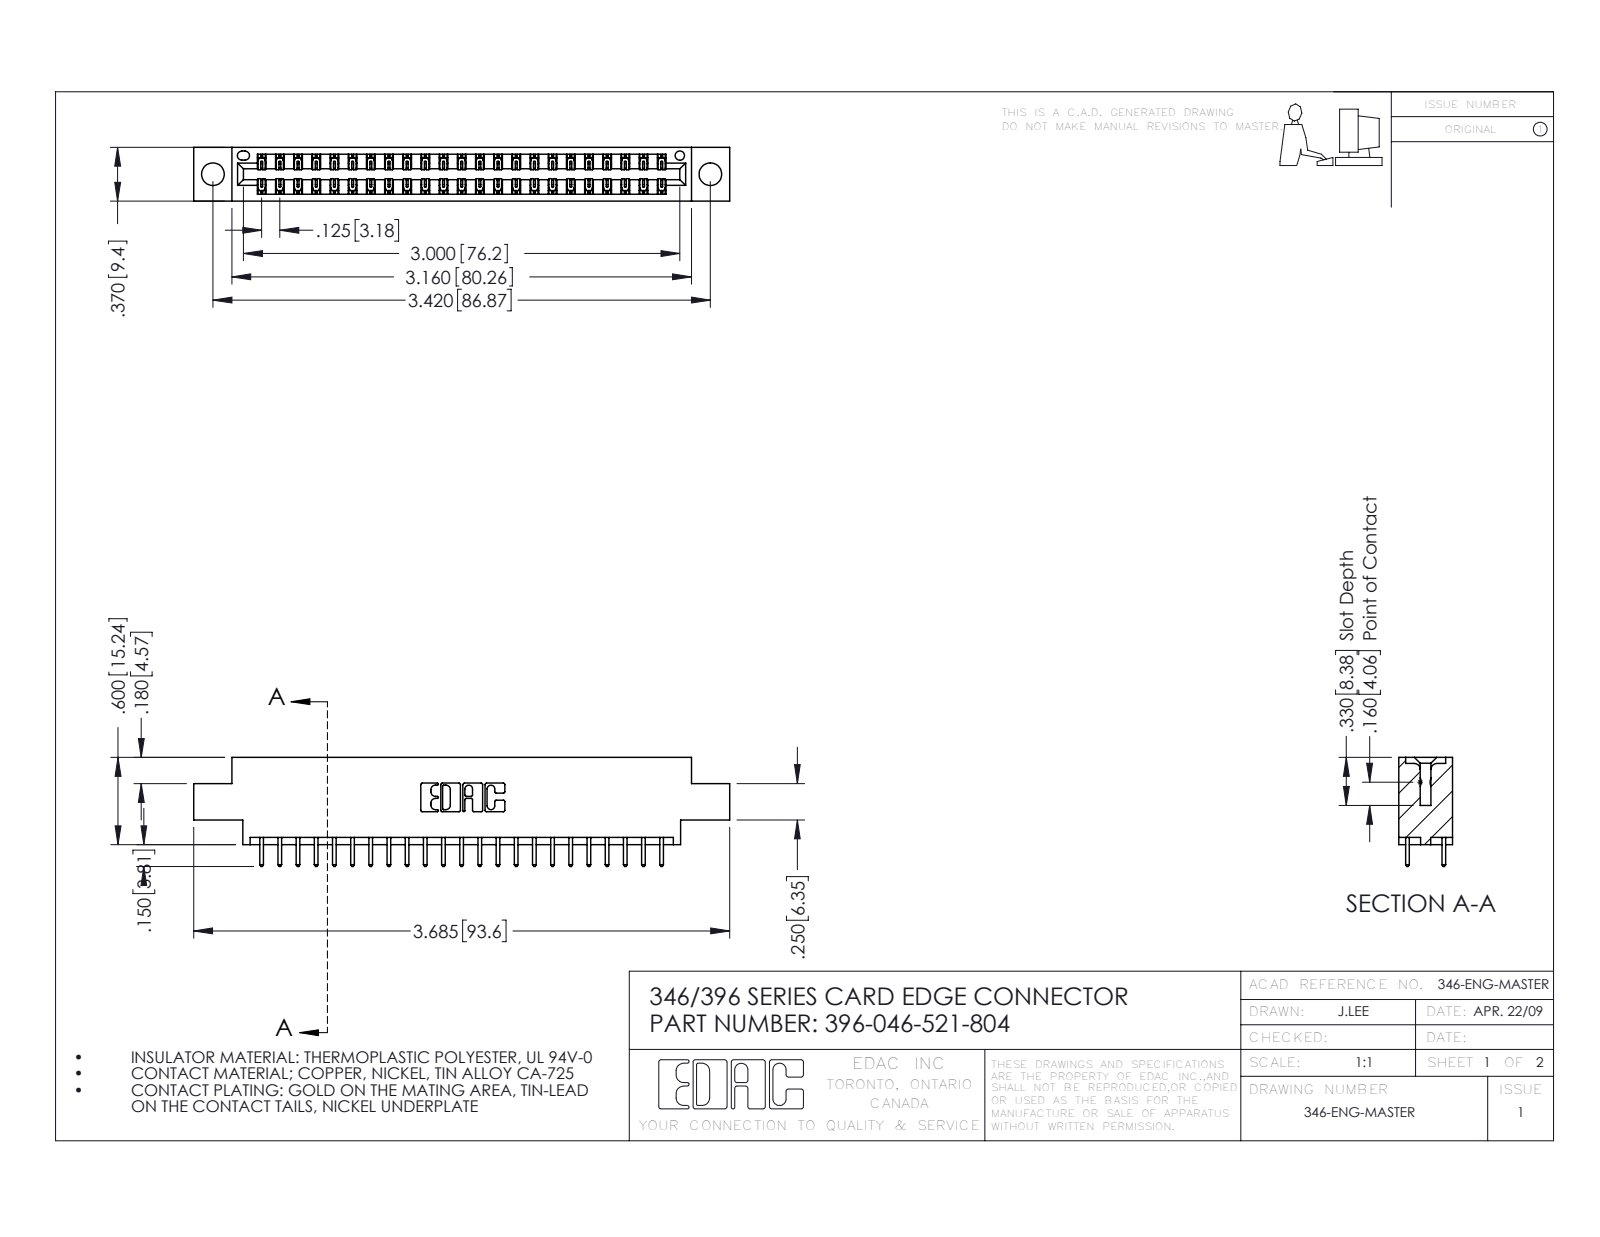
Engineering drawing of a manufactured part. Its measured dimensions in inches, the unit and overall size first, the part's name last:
Units: inches
Overall size (bounding box): 3.685 × 0.75 × 0.37
Round holes (diameter × count): ⌀0.156 ×2, ⌀0.064 ×1
Partial cylindrical surfaces — rounded edges, fillets, slot ends (radius × count): R0.006 ×69, R0.01 ×46, R0.01 ×22, R0.007 ×6, R0.031 ×6, R0.026 ×3, R0.014 ×2, R0.022 ×2
Main face-to-face distances: 0.048, 0.322, 0.37, 0.25, 0.072, 0.298, 0.025, 0.275, 0.148, 0.222
Hole centre spacings: 0.246, 3.212, 3.42
Volume: 0.532 in³ · Surface area: 17.91 in²
Bodies: 47 solids, 2518 faces (1690 planar, 828 cylindrical, 0 other)
Part name (STEP PRODUCT): 345-292-001_345-293-121; 346 Part_0.170 Offset - 0.156 Dia-TH; 396-046-521-804
STEP written by: SolidWorks 2016 (CONFIG_CONTROL_DESIGN)
